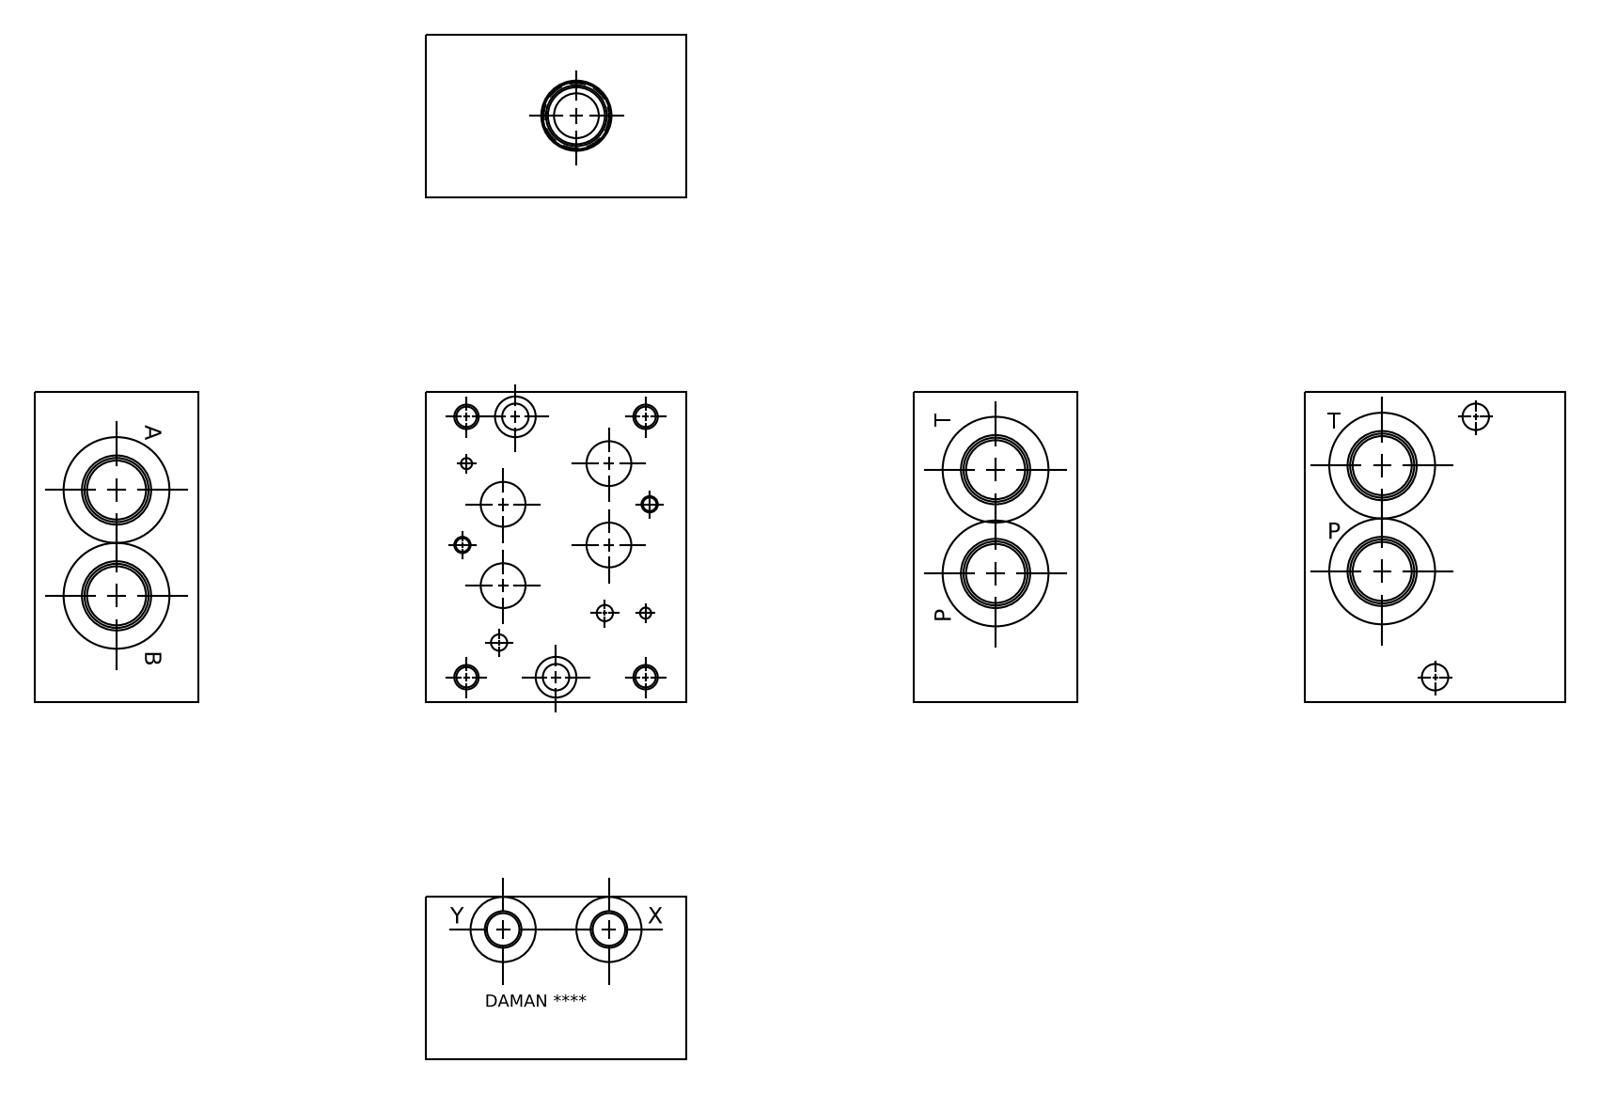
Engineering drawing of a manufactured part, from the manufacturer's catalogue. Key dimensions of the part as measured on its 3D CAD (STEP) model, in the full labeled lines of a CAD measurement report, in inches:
Part name (STEP PRODUCT): Part_AD07SPRVS12S_3D
STEP written by: Autodesk Inventor 2019 (AUTOMOTIVE_DESIGN)
Units: inches
Bodies: 1 solid, 613 faces (354 planar, 74 cylindrical, 185 other)
Overall size (bounding box): 4.75 × 4 × 2.5
Volume: 37.41 in³ · Surface area: 124 in²
Round holes (diameter × count): ⌀1.08 ×6, ⌀1.655 ×6, ⌀0.688 ×5, ⌀0.25 ×4, ⌀0.312 ×4, ⌀0.375 ×4, ⌀1.063 ×3, ⌀1.063 ×3, ⌀0.171 ×2, ⌀0.201 ×2, ⌀0.406 ×2, ⌀0.484 ×2
Partial cylindrical surfaces — rounded edges, fillets, slot ends (radius × count): R0.453 ×4, R0.491 ×4
Main face-to-face distances: 2.5, 4.75, 4, 0.031, 3.969, 0.15, 2.35, 3.938, 4.719, 0.75
Hole centre spacings: 1.741, 0.884, 0.884, 1.25, 1.375, 1.625, 2.25, 2.574
